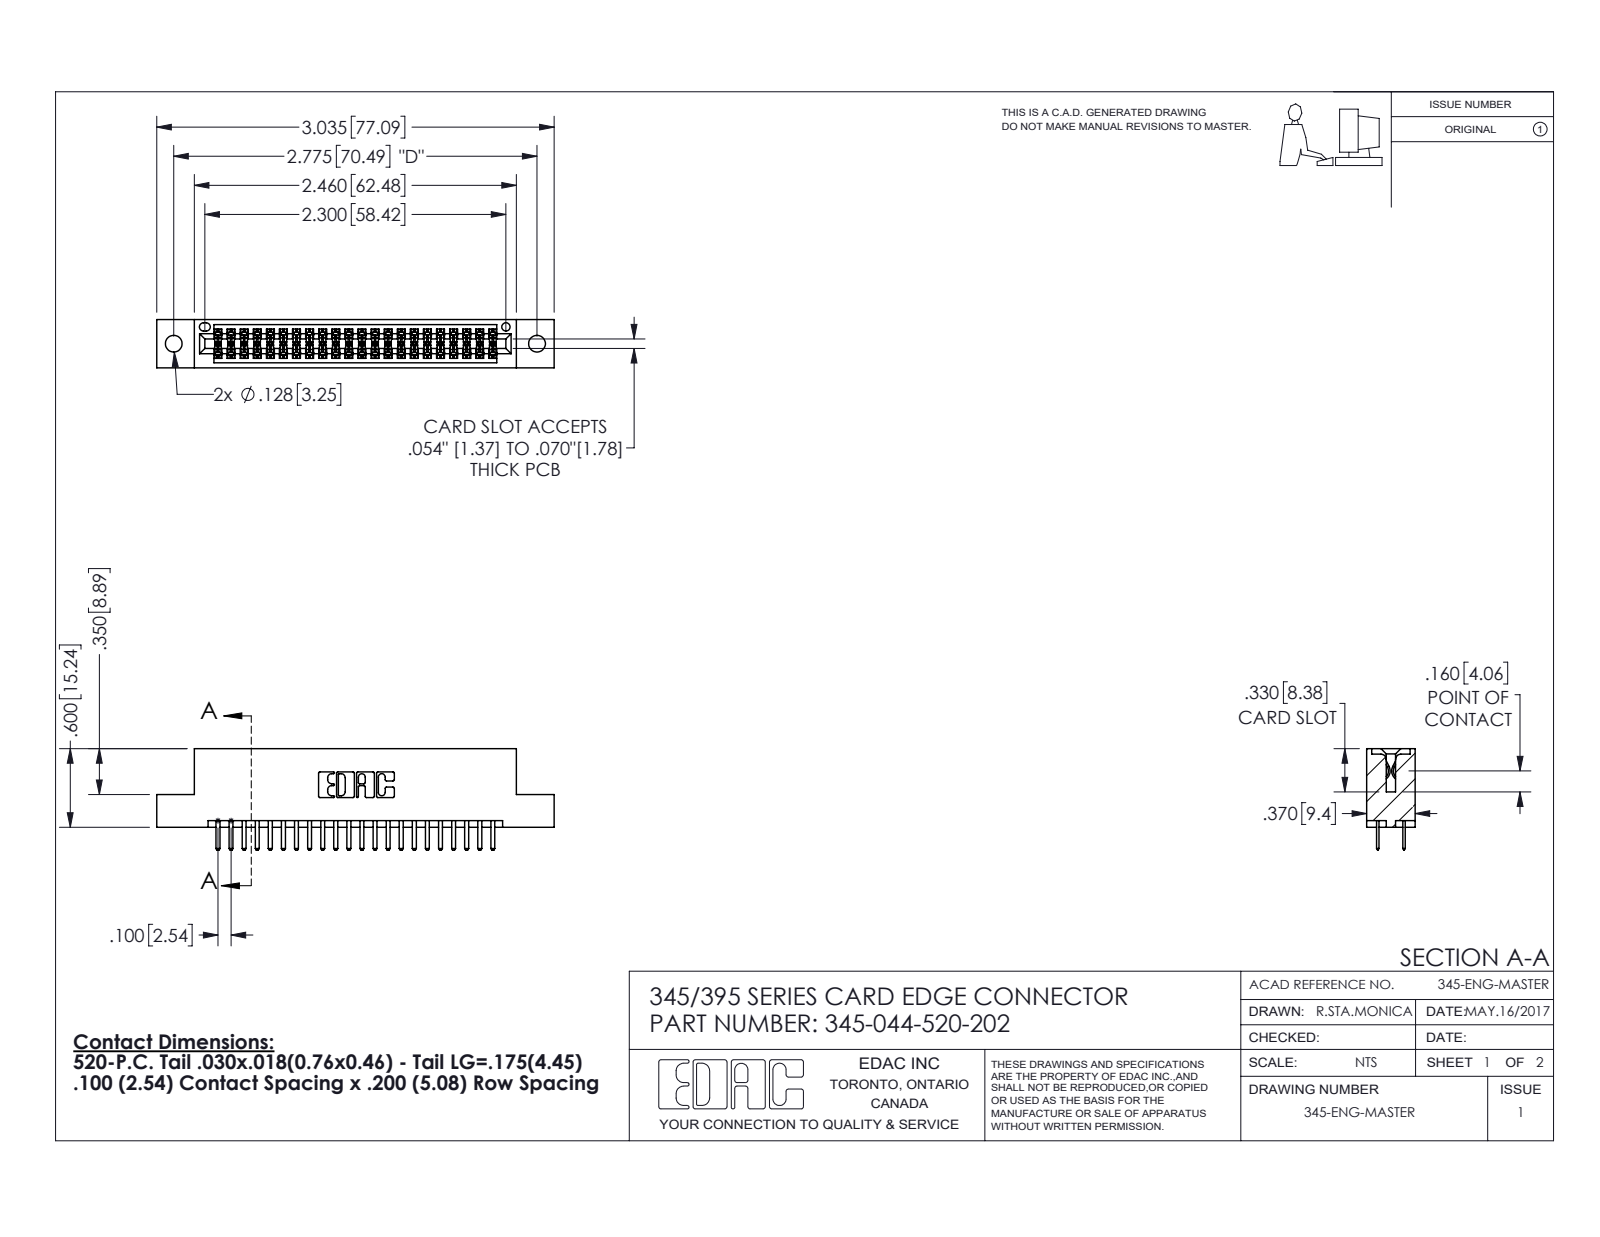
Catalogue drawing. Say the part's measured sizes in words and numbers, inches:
The part is named "345 Part_Flush Mounting Lugs - 0.128 Dia; 345-292-001_345-293-120; 345-044-520-202". Its 3-D file was written by "SolidWorks 2016 (CONFIG_CONTROL_DESIGN)". It is 45 solids with 2502 faces: 1620 planar, 882 cylindrical and 0 other. Overall it measures 3.035 by 0.775 by 0.37 inches. Its volume is 0.442 cubic inches and its surface area 15.52 square inches. Round holes: 2 of diameter 0.128, 1 of diameter 0.064. Partial cylindrical surfaces (rounded edges, fillets, slot ends): 66 of radius 0.006, 48 of radius 0.01, 22 of radius 0.01, 6 of radius 0.007, 6 of radius 0.031, 3 of radius 0.026, 2 of radius 0.014, 2 of radius 0.019. The main face-to-face distances are 0.298, 0.072, 0.2, 0.37, 0.098, 0.272, 0.025, 0.225, 0.022, 0.072. The hole center spacings are 0.27, 2.541, 2.775.
